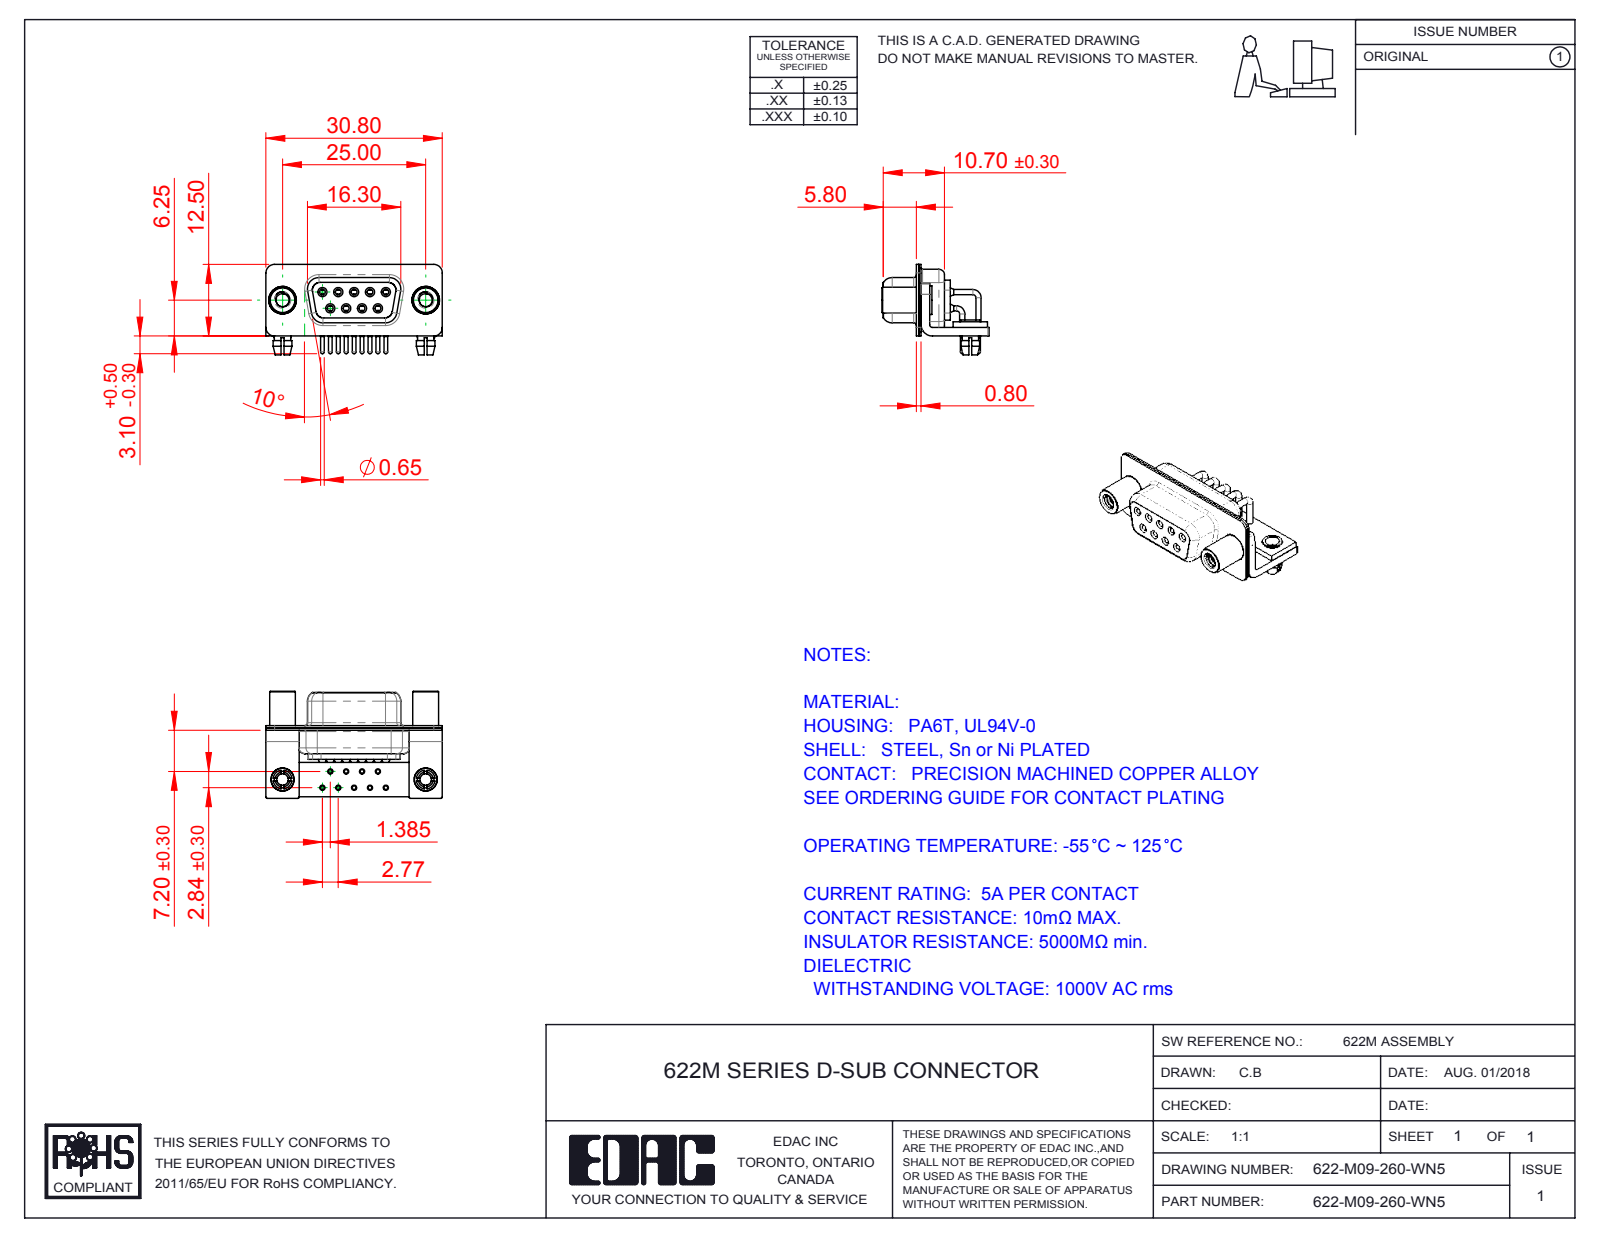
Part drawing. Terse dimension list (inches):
name: 622M Shell Rear_09 Contacts; 622-M09-260-WN5; 622M Shell Front_09 Contacts; 622M Housing_09 Contacts (+6 more)
written by: SolidWorks 2016 (CONFIG_CONTROL_DESIGN)
unit: in
bodies: 19 solids, 966 faces (278 planar, 458 cylindrical, 230 other)
size: 1.213 × 0.736 × 0.622
volume: 0.141 in³; area: 9.43 in²
holes: 11× ⌀0.079, 9× ⌀0.035, 9× ⌀0.039, 9× ⌀0.043, 9× ⌀0.067, 9× ⌀0.071, 2× ⌀0.089, 2× ⌀0.098, 2× ⌀0.126, 2× ⌀0.157, 2× ⌀0.189
bosses: 9× ⌀0.063, 9× ⌀0.059, 9× ⌀0.035, 9× ⌀0.026, 2× ⌀0.197, 2× ⌀0.193, 2× ⌀0.177, 2× ⌀0.157
rounds: 16× R0.01, 16× R0.059, 13× R0.079, 8× R0.053, 8× R0.063, 5× R0.02, 4× R0.024, 4× R0.026
face distances: 0.016, 0.031, 0.091, 0.059, 0.075, 0.039, 0.368, 0.057, 0.335, 0.352
hole spacings: 0.124, 0.109, 0.218, 0.198, 0.198, 0.327, 0.294, 0.295
